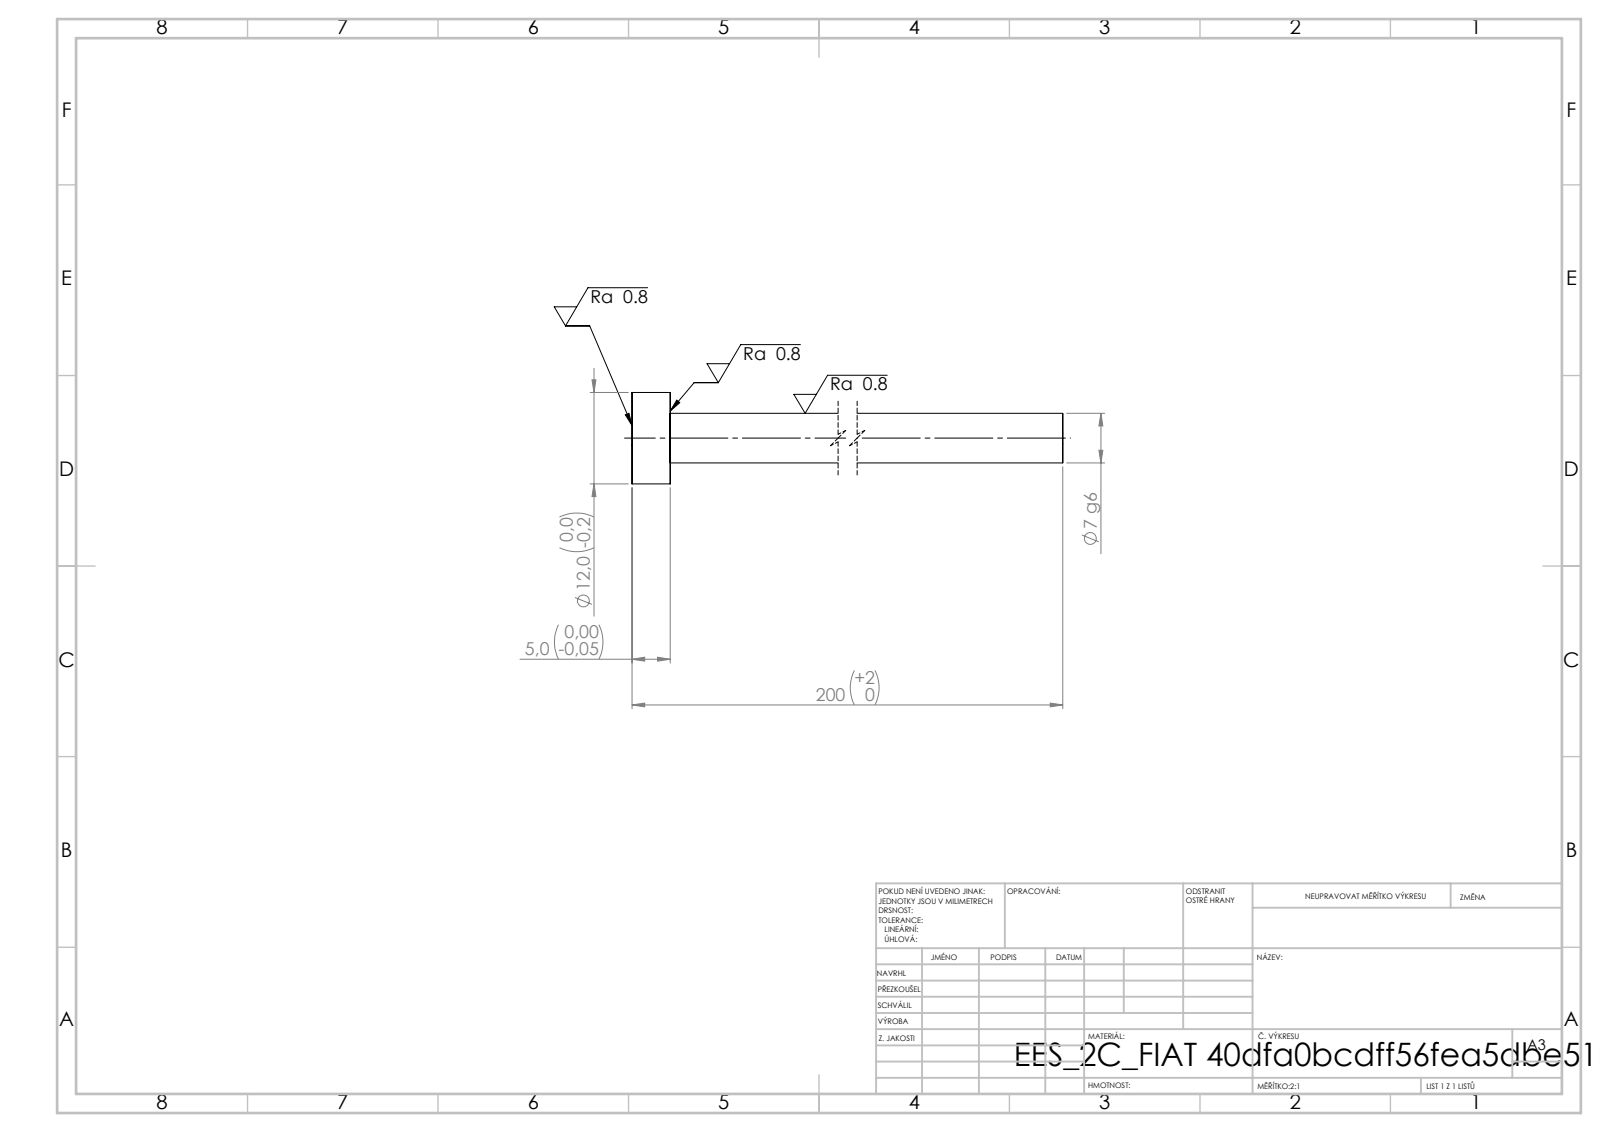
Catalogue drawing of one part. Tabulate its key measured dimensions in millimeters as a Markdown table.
| quantity | value |
| --- | --- |
| STEP written by | SolidWorks 2019 (CONFIG_CONTROL_DESIGN) |
| units | millimeters |
| bodies | 1 solid, 7 faces (3 planar, 4 cylindrical, 0 other) |
| overall size | 200 × 12 × 12 |
| volume | 7 036 mm³ |
| surface area | 4 397 mm² |
| round bosses / shafts (diameter × count) | 12 × 1, 6.5 × 1 |
| main face-to-face distances | 5, 200, 195 |
